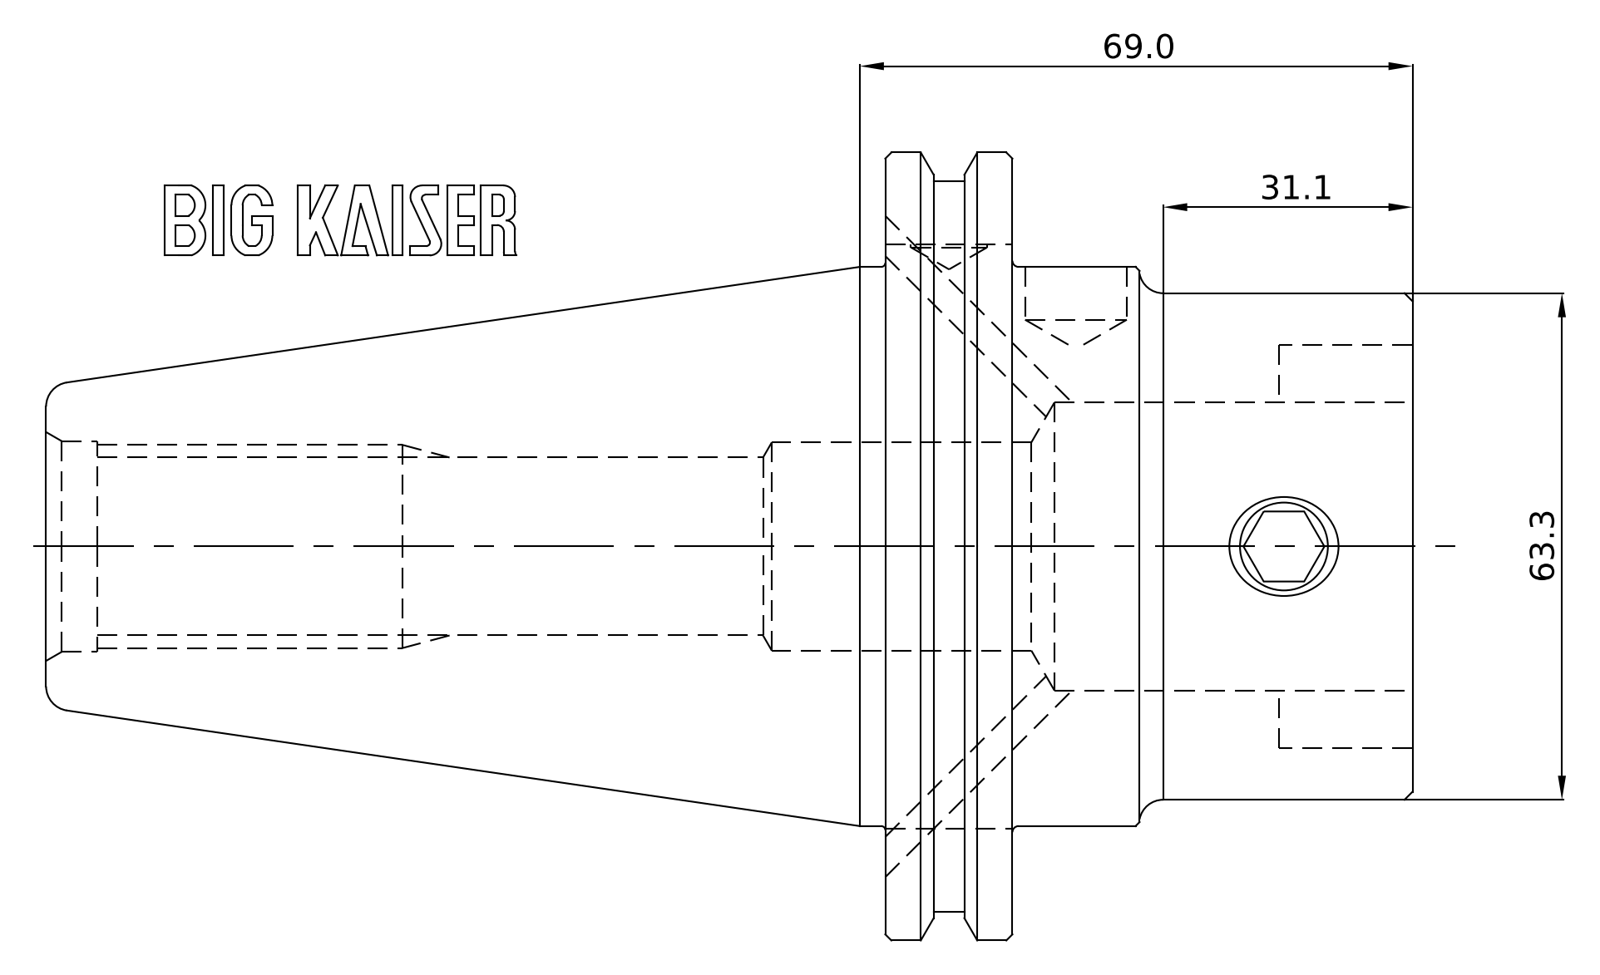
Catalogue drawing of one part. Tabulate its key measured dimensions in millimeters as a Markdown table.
| quantity | value |
| --- | --- |
| part name | 11.326.962 |
| STEP written by | SolidWorks 2021 (CONFIG_CONTROL_DESIGN) |
| units | millimeters |
| bodies | 1 solid, 16 faces (7 planar, 6 cylindrical, 3 other) |
| overall size | 170.6 × 98.43 × 98.43 |
| volume | 550 156 mm³ |
| surface area | 47 756 mm² |
| round bosses / shafts (diameter × count) | 98.43 × 1, 91.29 × 1, 69.85 × 1, 63.5 × 1 |
| main face-to-face distances | 17.55, 49.95, 67.5, 170.6, 120.65, 103.1, 34, 15.95, 33.5, 136.6 |
